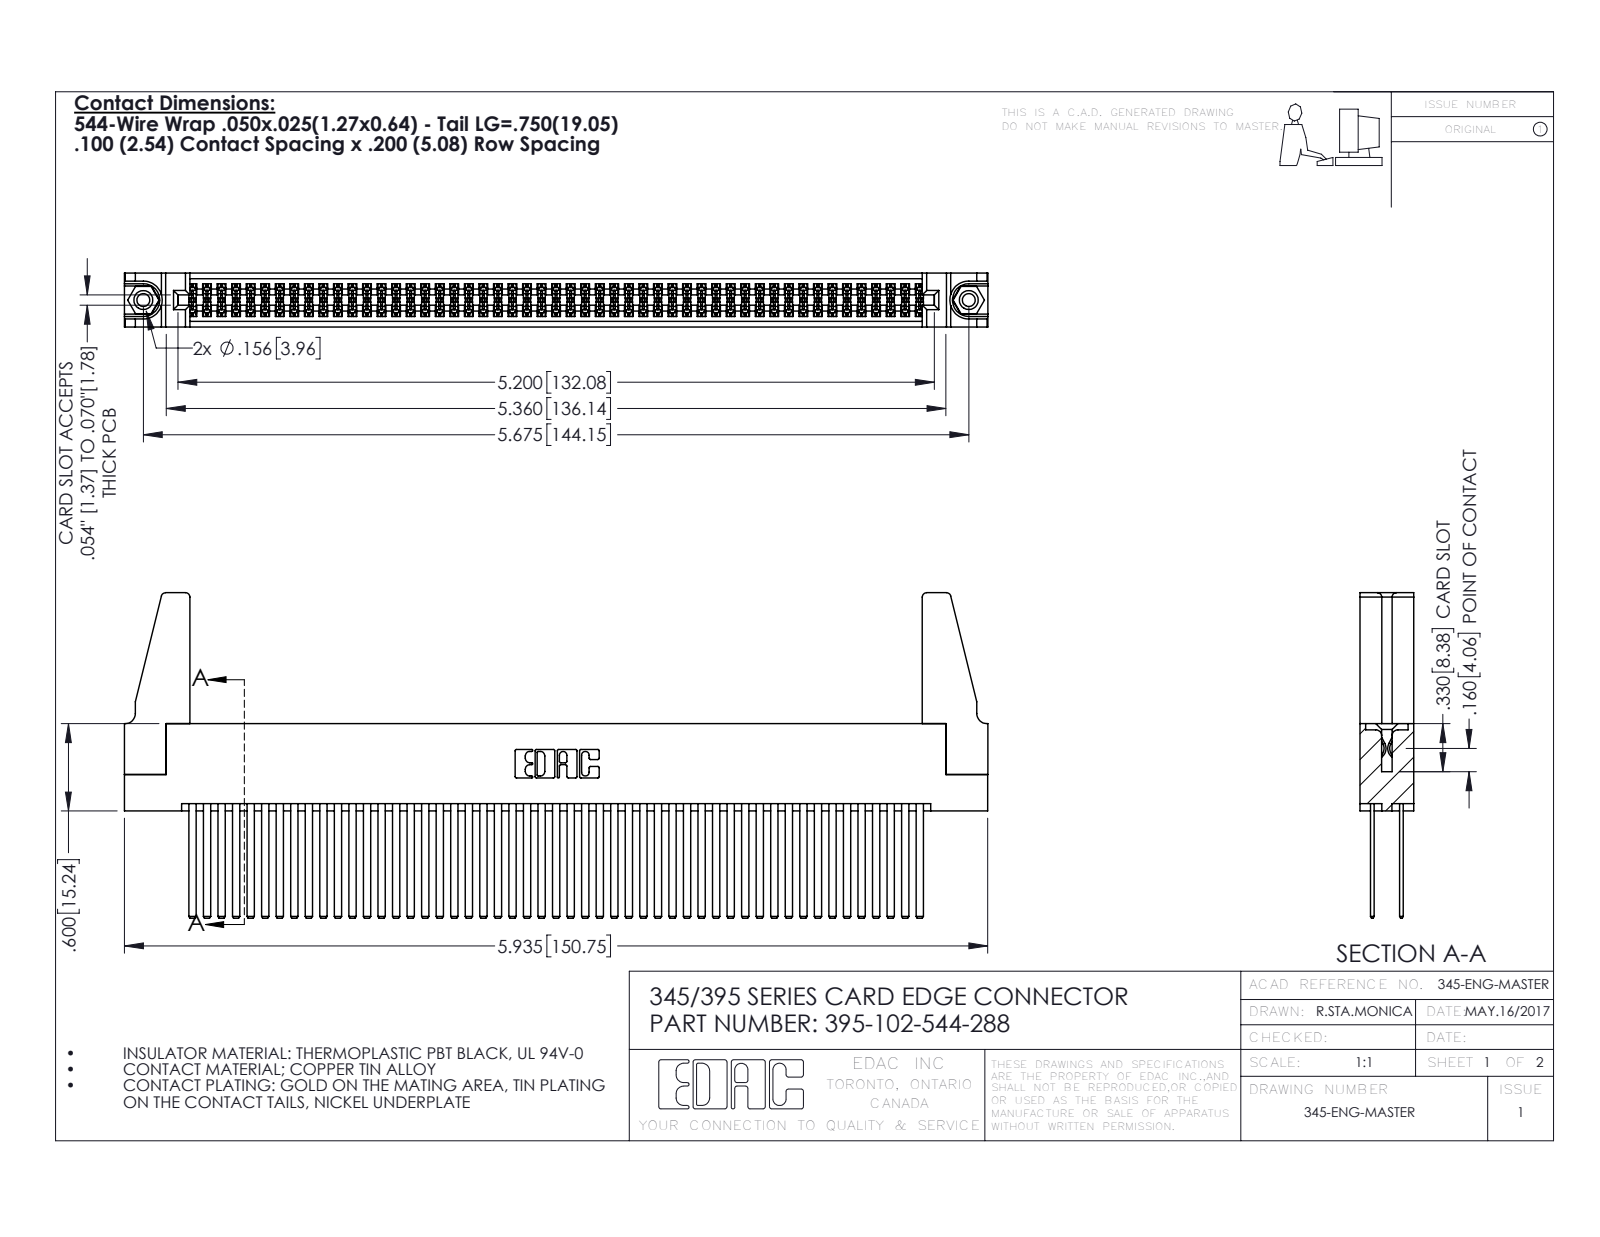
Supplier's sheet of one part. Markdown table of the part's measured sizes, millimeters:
| quantity | value |
| --- | --- |
| part name | 345-220-078_345-220-088; 345 Part_Flush Mounting Lugs - 0.156 Dia-TH; 345-250-001_345-250-001-102; 345-292-001_345-293-144 (+1 more) |
| STEP written by | SolidWorks 2016 (CONFIG_CONTROL_DESIGN) |
| units | millimeters |
| bodies | 107 solids, 4738 faces (3110 planar, 1612 cylindrical, 16 other) |
| overall size | 150.8 × 56.8 × 9.4 |
| volume | 19 420 mm³ |
| surface area | 31 370 mm² |
| round holes (diameter × count) | 2.3 × 2, 3.2 × 2, 4 × 2, 1.6 × 1 |
| round bosses / shafts (diameter × count) | 3.9 × 2 |
| partial cylindrical surfaces (radius × count) | 0.2 × 153, 0.3 × 22, 0.8 × 8, 0.2 × 6, 0.8 × 6, 0.7 × 3, 0.4 × 2, 0.5 × 2 |
| main face-to-face distances | 1.8, 7.6, 5.1, 2.5, 6.9, 0.6, 5.7, 9.4, 4.4, 3.8 |
| hole center spacings | 6.9, 138.2, 144.1 |
